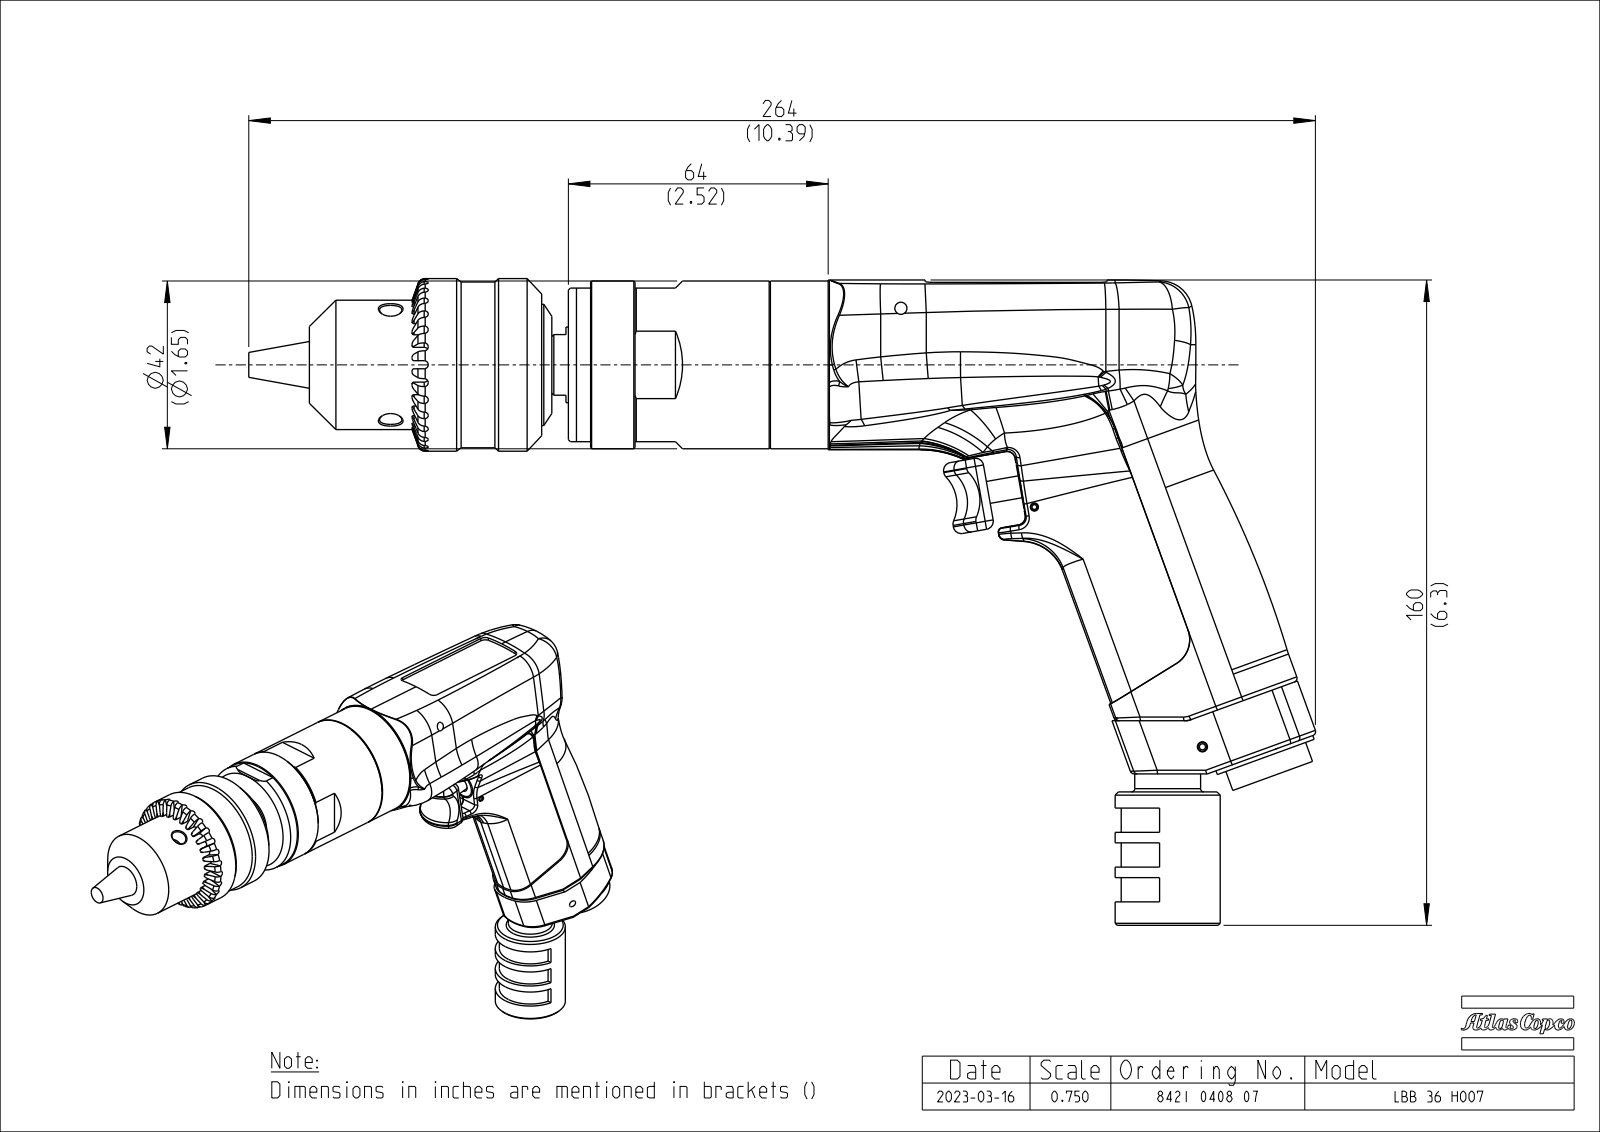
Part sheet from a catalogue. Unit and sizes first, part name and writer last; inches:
Units: inches
Overall size (bounding box): 10.395 × 6.298 × 1.928
Round holes (diameter × count): ⌀0.079 ×3, ⌀0.217 ×3, ⌀0.047 ×1, ⌀0.098 ×1, ⌀0.118 ×1, ⌀0.205 ×1, ⌀0.453 ×1, ⌀0.496 ×1, ⌀0.591 ×1, ⌀0.646 ×1, ⌀0.886 ×1, ⌀0.906 ×1
Round bosses / shafts (diameter × count): ⌀1.681 ×1, ⌀1.654 ×1, ⌀1.634 ×1, ⌀1.614 ×1, ⌀1.26 ×1, ⌀1.181 ×1, ⌀1.024 ×1, ⌀1.004 ×1
Partial cylindrical surfaces — rounded edges, fillets, slot ends (radius × count): R0.02 ×60, R0.039 ×46, R0.079 ×16, R0.118 ×4, R0.157 ×2, R0.276 ×2, R0.315 ×2, R1.693 ×2
Main face-to-face distances: 0.051, 1.142, 0.039, 0.031, 0.02, 1.496, 1.319, 0.177, 0.236, 0.079
Hole centre spacings: 0.391, 0.383, 2.332, 2.852, 5.002, 5.183, 6.423, 8.741
Volume: 22.78 in³ · Surface area: 88.5 in²
Bodies: 3 solids, 873 faces (183 planar, 232 cylindrical, 458 other)
Part name (STEP PRODUCT): EXT_COMP_SW0004
STEP written by: CREO PARAMETRIC BY PTC INC, 2020281 (CONFIG_CONTROL_DESIGN)
